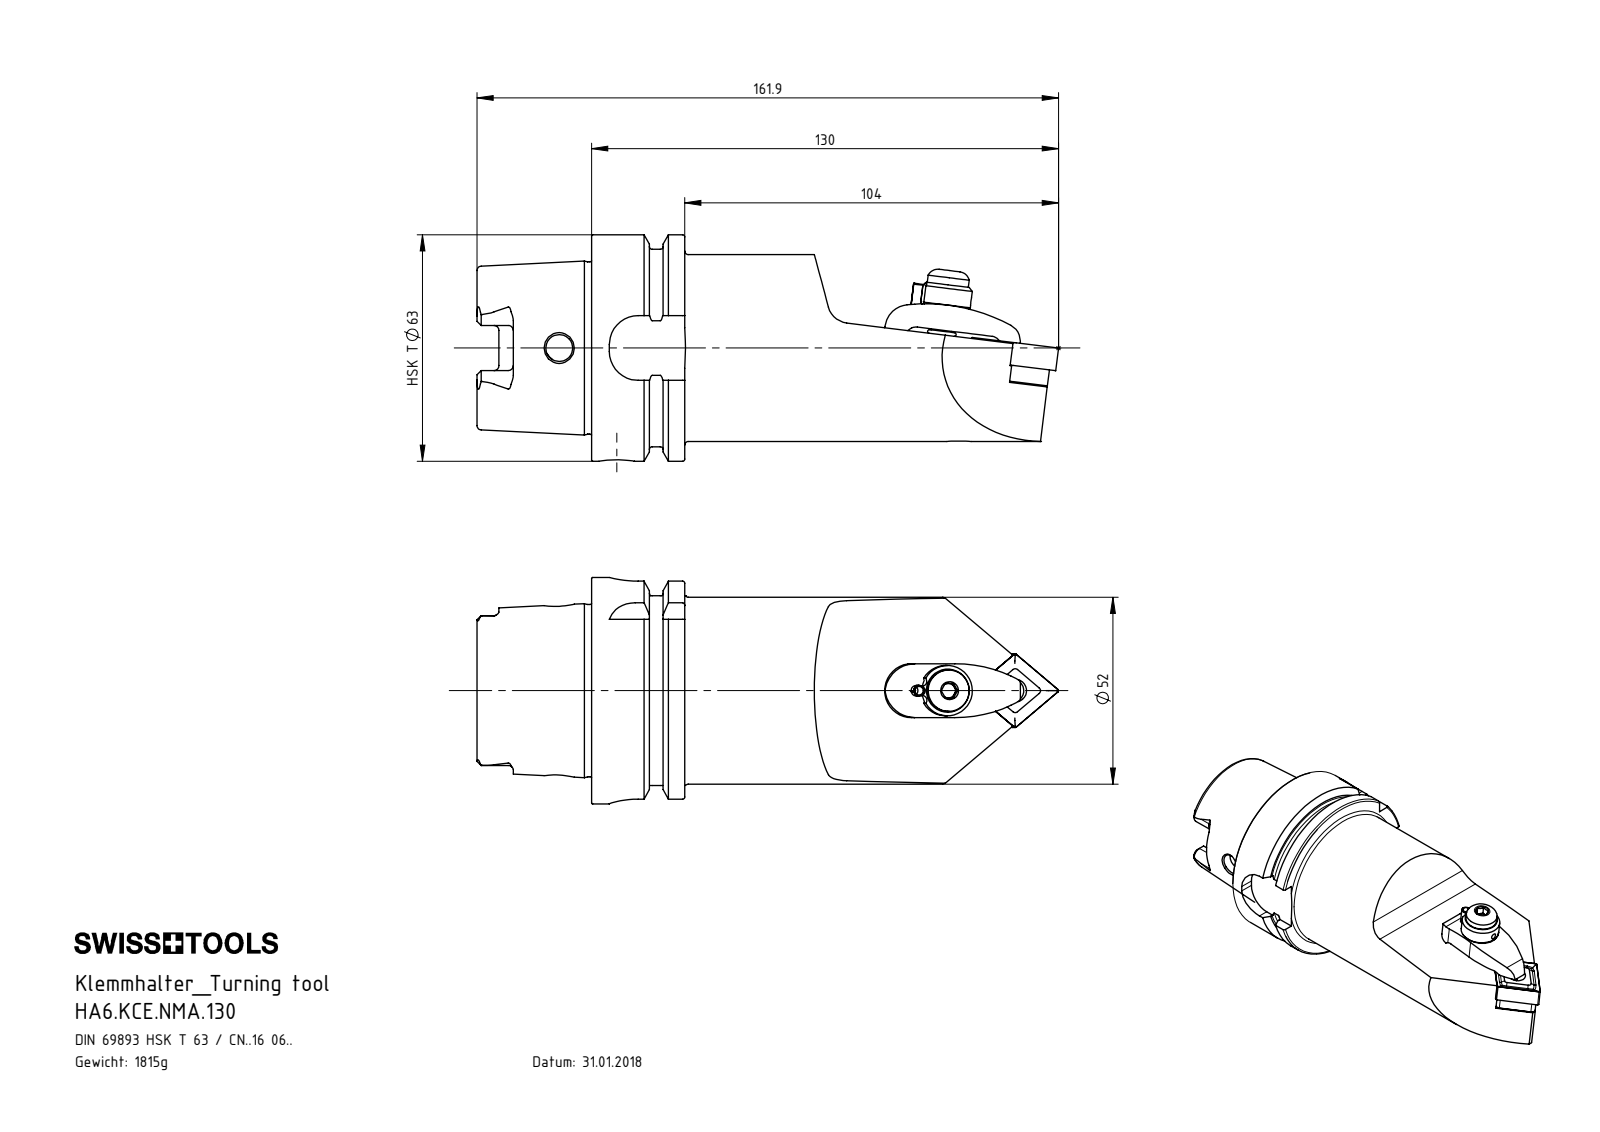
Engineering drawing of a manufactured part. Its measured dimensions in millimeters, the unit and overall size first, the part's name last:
Units: millimetres
Overall size (bounding box): 161.9 × 63 × 63
Round holes (diameter × count): ⌀2 ×3, ⌀4.2 ×3, ⌀5 ×3, ⌀7 ×2, ⌀2.4 ×1, ⌀3 ×1, ⌀4 ×1, ⌀6.2 ×1, ⌀6.35 ×1, ⌀7.5 ×1, ⌀8.05 ×1, ⌀8.4 ×1
Round bosses / shafts (diameter × count): ⌀5 ×2, ⌀3 ×2, ⌀63 ×1, ⌀54.95 ×1, ⌀52 ×1, ⌀47.94 ×1, ⌀14 ×1, ⌀11.5 ×1
Partial cylindrical surfaces — rounded edges, fillets, slot ends (radius × count): R1.5 ×7, R0.45 ×6, R1.4 ×6, R0.4 ×4, R0.79 ×4, R8 ×4, R0.79 ×2, R2 ×2
Main face-to-face distances: 25.95, 16, 9.95, 6.06, 31.9, 41.85, 57.85, 15.06, 52.8, 4.77
Hole centre spacings: 7.99, 8.19, 9.81, 17.8, 20.41, 20.6, 28.4, 28.59
Volume: 230 120 mm³ · Surface area: 43 087 mm²
Bodies: 11 solids, 460 faces (125 planar, 150 cylindrical, 185 other)
Part name (STEP PRODUCT): ISO 13337 - 3 x 12_PreviewCfg; WCE-ER2.001.012_A; WCC-ER5.102.012_B; WCE-ER2.101.004_A (+7 more)
STEP written by: SolidWorks 2017 (CONFIG_CONTROL_DESIGN)
